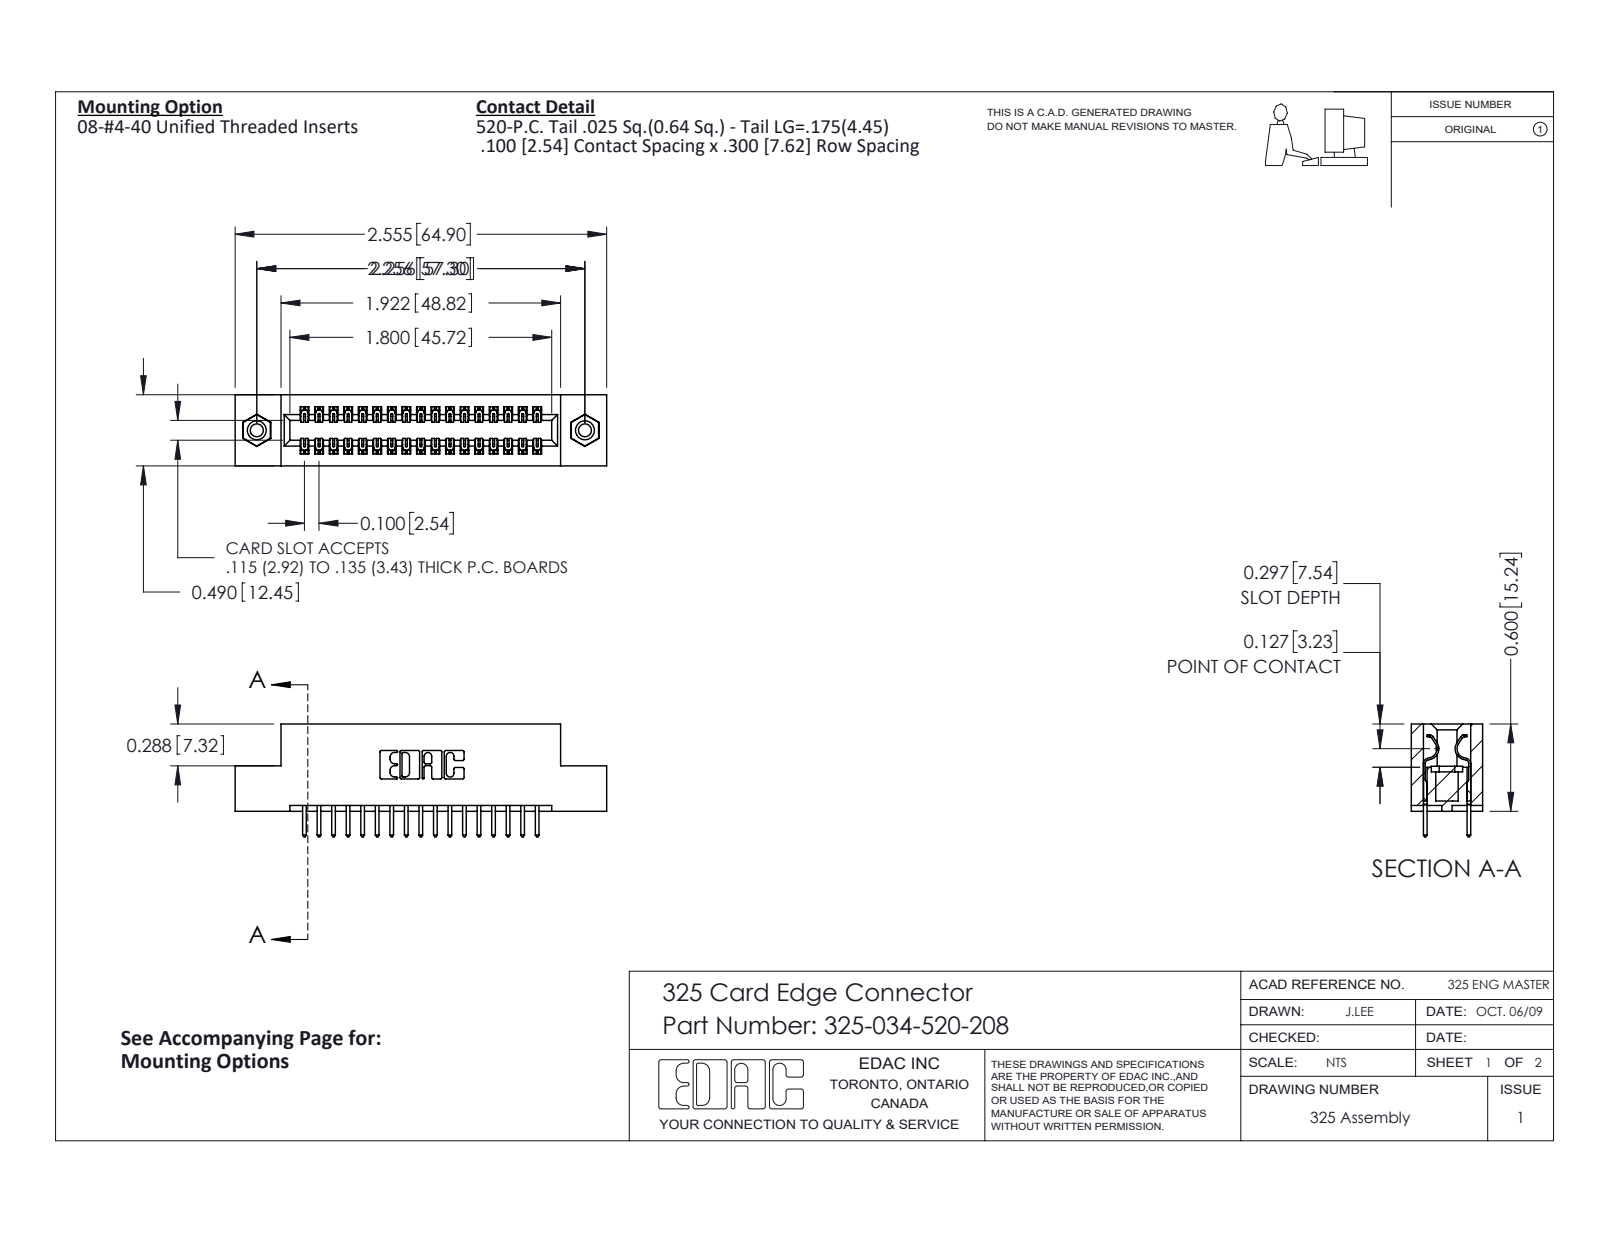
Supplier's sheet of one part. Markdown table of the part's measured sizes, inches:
| quantity | value |
| --- | --- |
| part name | 325-034-520-208; 325-292-001_325-293-120; 345-250-001_345-250-003-102; 325 Part_TI |
| STEP written by | SolidWorks 2016 (CONFIG_CONTROL_DESIGN) |
| units | inches |
| bodies | 37 solids, 1942 faces (1326 planar, 600 cylindrical, 16 other) |
| overall size | 2.555 × 0.775 × 0.49 |
| volume | 0.497 in³ |
| surface area | 14.27 in² |
| round holes (diameter × count) | 0.089 × 2, 0.125 × 2, 0.16 × 2 |
| round bosses / shafts (diameter × count) | 0.155 × 2 |
| partial cylindrical surfaces (radius × count) | 0.006 × 51, 0.01 × 34, 0.01 × 22, 0.007 × 6, 0.031 × 6, 0.026 × 3, 0.014 × 2, 0.022 × 2 |
| main face-to-face distances | 0.083, 0.407, 0.3, 0.49, 0.107, 0.383, 0.025, 0.325, 0.6, 0.04 |
| hole center spacings | 2.256 |
